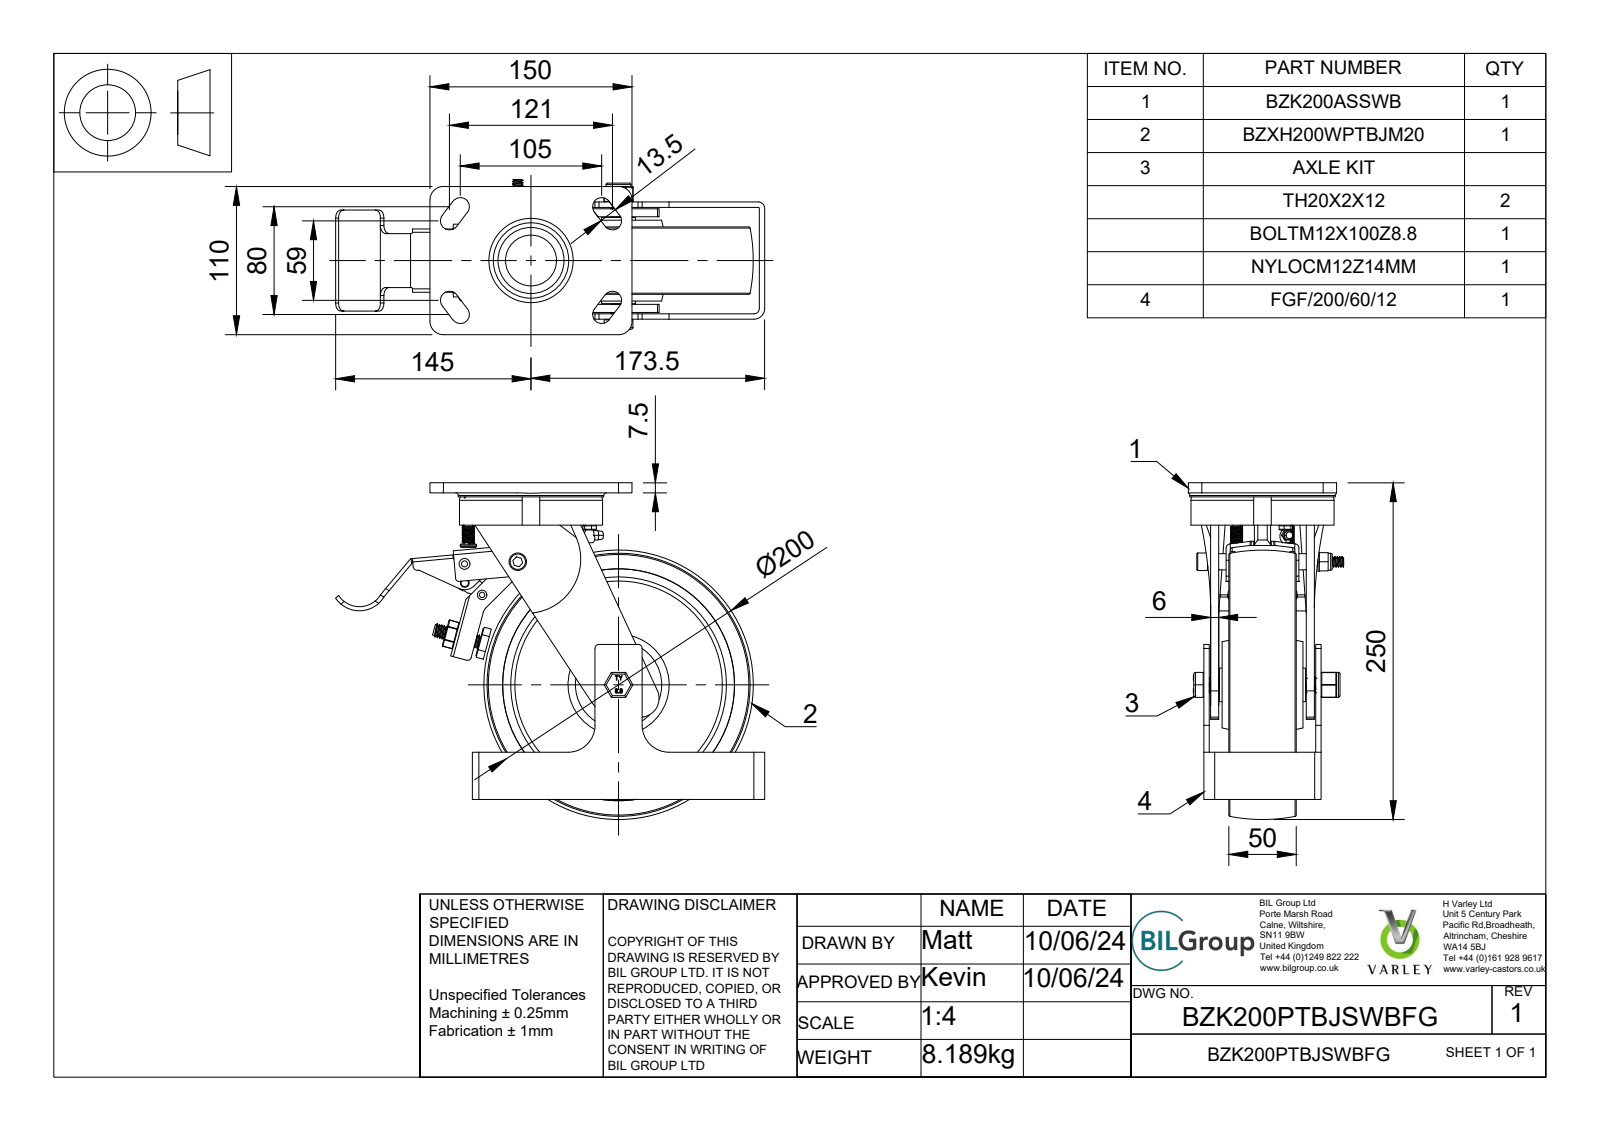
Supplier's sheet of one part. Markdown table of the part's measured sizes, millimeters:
| quantity | value |
| --- | --- |
| part name | BZK200PTBJSWBFG v3; BZK200ASSWB v1; FABRICATED STEEL TOP PLATE; FABRICATED STEEL FORKS (+8 more) |
| STEP written by | Autodesk Translation Framework v13.14.0.145 (AUTOMOTIVE_DESIGN) |
| units | millimeters |
| bodies | 57 solids, 1496 faces (595 planar, 442 cylindrical, 459 other) |
| overall size | 318.5 × 250 × 115.22 |
| volume | 1 463 000 mm³ |
| surface area | 457 493 mm² |
| round holes (diameter × count) | 6 × 5, 10 × 2, 5 × 1, 8 × 1, 12 × 1, 12.2 × 1, 13 × 1, 14 × 1, 20 × 1, 28.5 × 1, 30.8 × 1, 32 × 1 |
| round bosses / shafts (diameter × count) | 12 × 3, 8 × 2, 108 × 1, 107 × 1, 40.8 × 1, 31.3 × 1, 27 × 1, 25 × 1 |
| partial cylindrical surfaces (radius × count) | 0.5 × 50, 1 × 11, 6 × 8, 6.75 × 8, 1.25 × 6, 2.5 × 5, 3 × 5, 10 × 5 |
| main face-to-face distances | 4, 7.5, 68.5, 39.5, 35.5, 47.5, 43.5, 83, 14.5, 21 |
| hole center spacings | 50.23, 14.12, 15.62, 26.42, 36.19, 38, 39.54, 42.39 |
